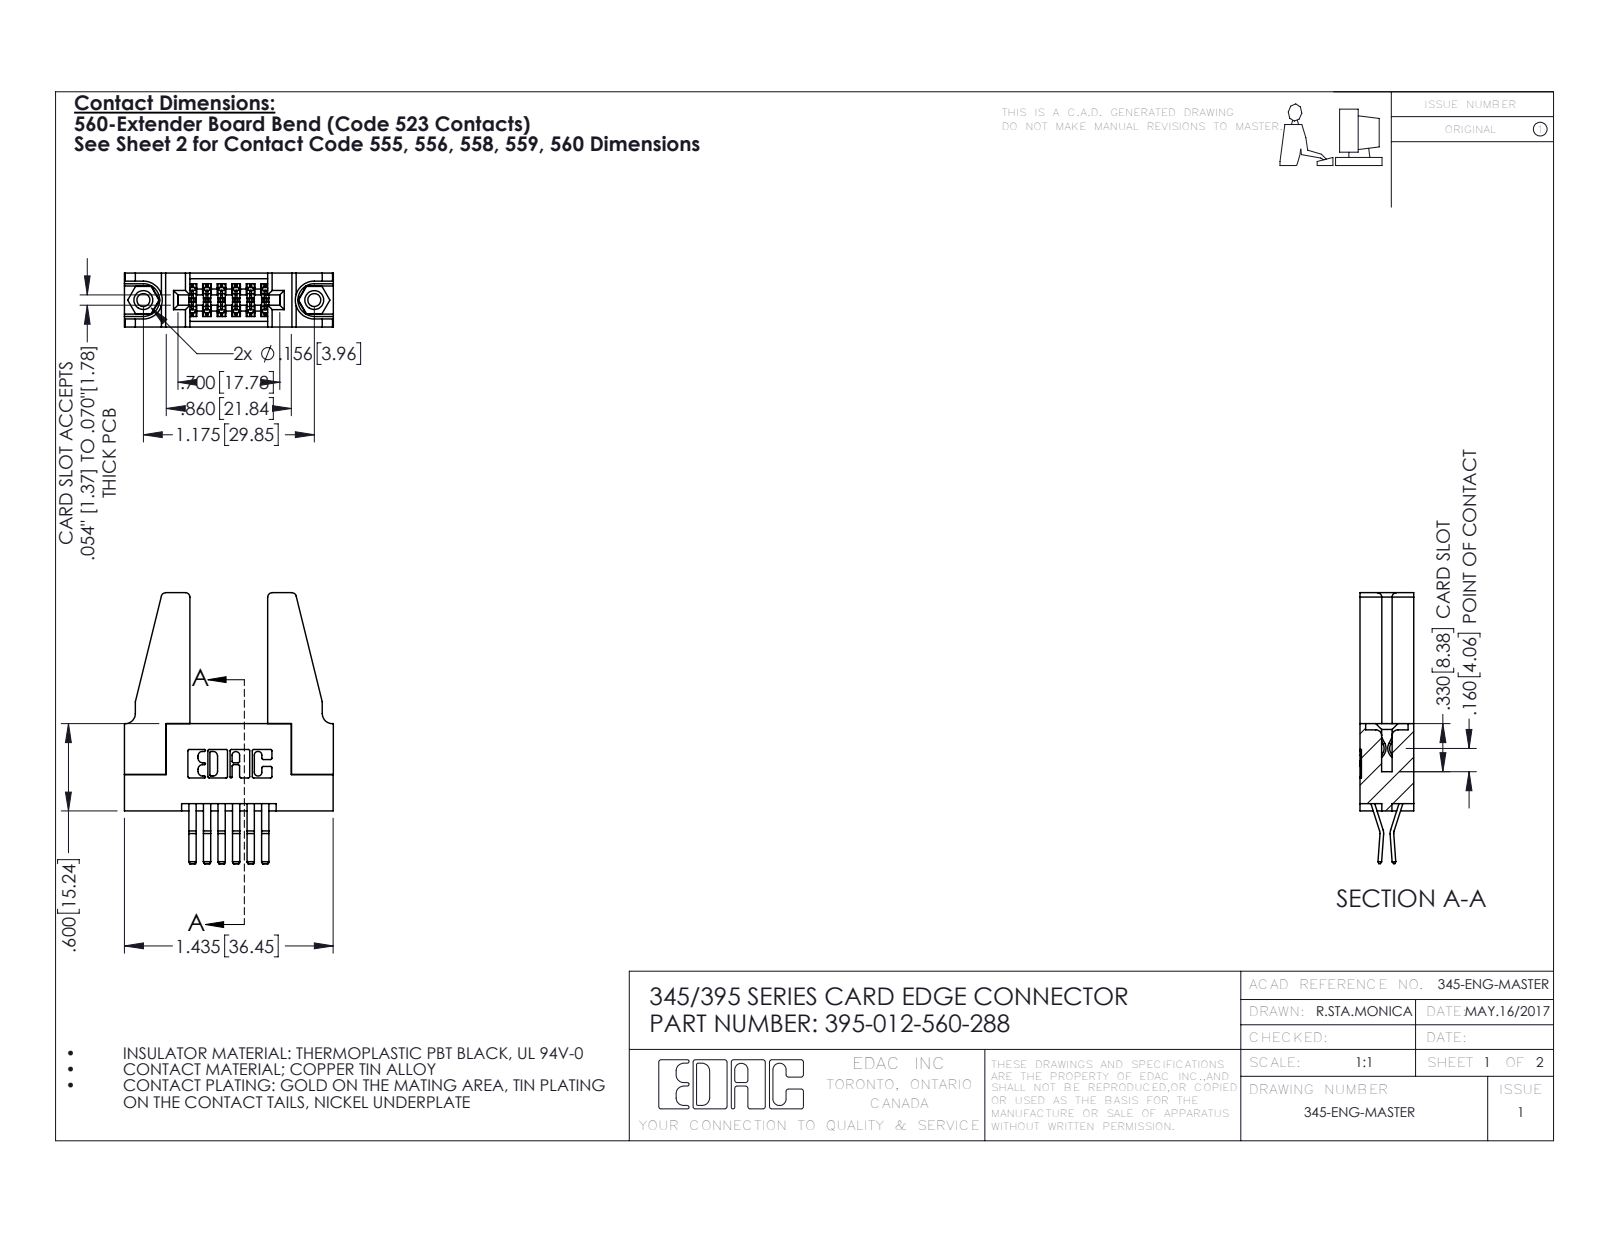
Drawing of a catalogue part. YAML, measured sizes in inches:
part_name: "345-292-001_560 Tail; 345 Part_Flush Mounting Lugs - 0.156 Dia-TH; 345-250-001_345-250-001-102; 345-220-078_345-220-088 (+1 more)"
step_written_by: "SolidWorks 2016 (CONFIG_CONTROL_DESIGN)"
units: inches
bodies: {solids: 17, faces: 874, planar: 548, cylindrical: 310, other: 16}
overall_size: [1.862, 1.436, 0.37]
volume: 0.399
surface_area: 11.6
round_holes:
  - {diameter: 0.089, count: 2}
  - {diameter: 0.125, count: 2}
  - {diameter: 0.156, count: 2}
  - {diameter: 0.064, count: 1}
round_bosses_or_shafts:
  - {diameter: 0.155, count: 2}
partial_cylinders:
  - {radius: 0.01, count: 22}
  - {radius: 0.006, count: 18}
  - {radius: 0.03, count: 8}
  - {radius: 0.007, count: 6}
  - {radius: 0.031, count: 6}
  - {radius: 0.026, count: 3}
  - {radius: 0.01, count: 2}
  - {radius: 0.014, count: 2}
face_to_face_distances: [0.37, 0.072, 0.2, 0.298, 0.025, 0.698, 0.15, 0.148, 0.35, 0.225]
hole_center_spacings: [0.27, 0.946, 1.175]
